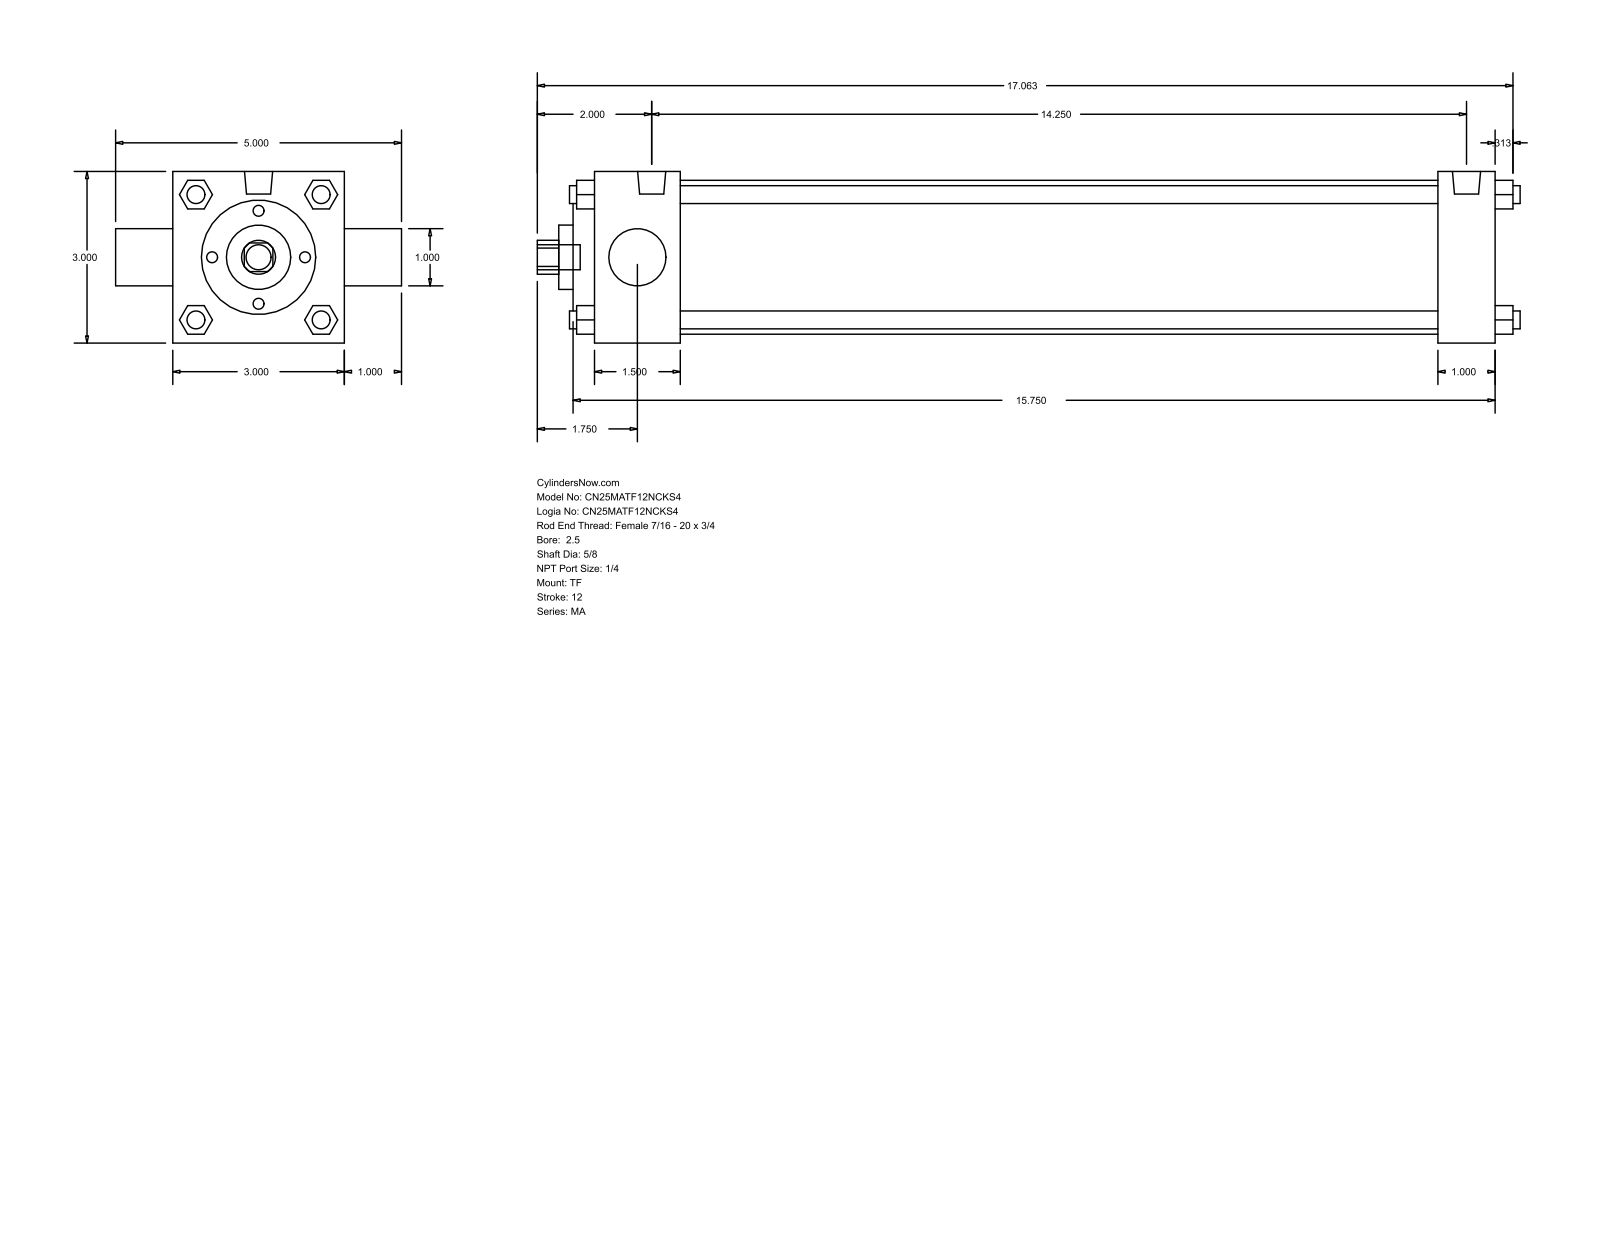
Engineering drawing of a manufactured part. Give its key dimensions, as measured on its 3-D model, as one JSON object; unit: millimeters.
{"part_name": "MA_TF__0250_0.625", "step_written_by": "GSSL Pune (CONFIG_CONTROL_DESIGN)", "units": "millimeters", "bodies": {"solids": 0, "faces": 122, "planar": 93, "cylindrical": 29, "other": 0}, "overall_size": [436.56, 127, 76.2], "round_holes": [[15.88, 1], [25.4, 1], [28.57, 1], [50.8, 1], [68.33, 1]], "round_bosses_or_shafts": [[7.94, 7], [12.49, 2], [11.11, 1]], "partial_cylinders_radius": [[7.54, 1]], "face_to_face_distances": [76.2, 400.05, 25.4, 38.1, 374.65, 336.55, 361.95, 12.7, 9.52, 47.62]}
